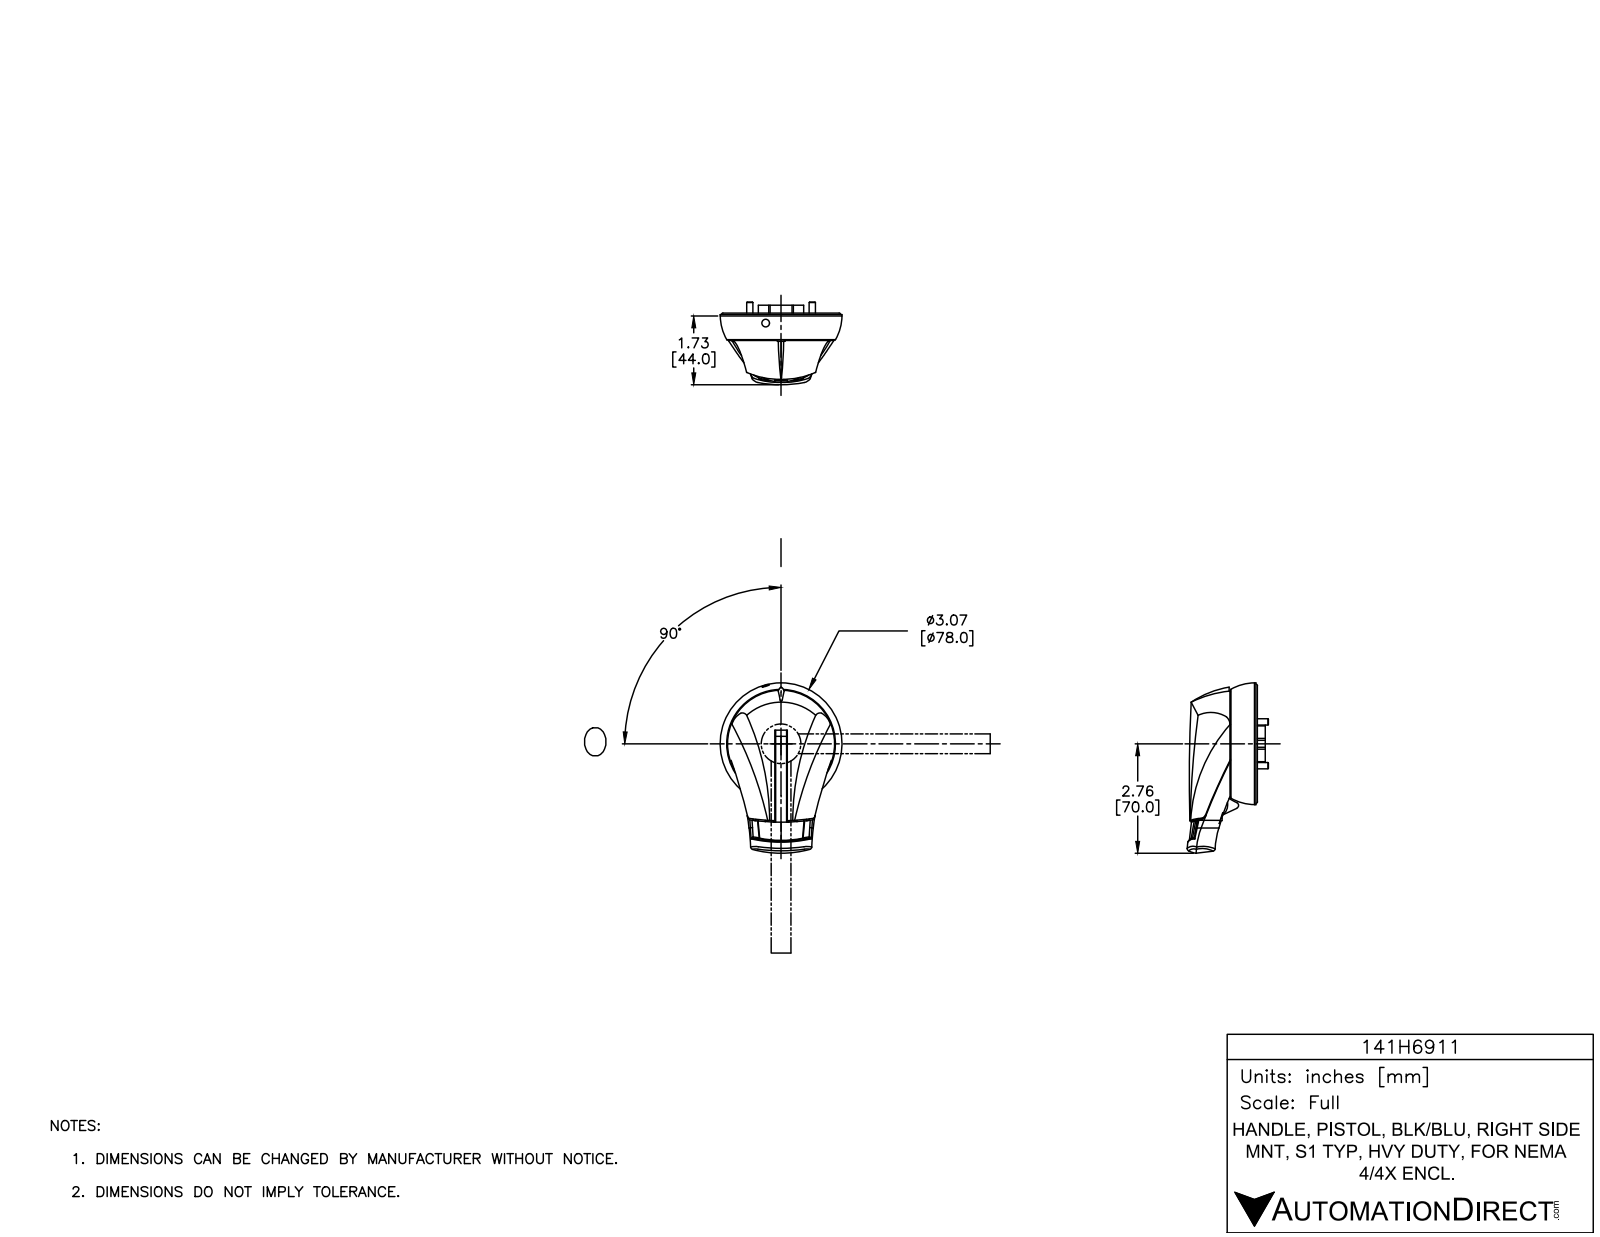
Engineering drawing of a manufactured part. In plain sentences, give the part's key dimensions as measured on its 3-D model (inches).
The part is named "141H6911". Its 3-D file was written by "SolidWorks 2015 (AUTOMOTIVE_DESIGN)". It is 8 solids with 1516 faces: 810 planar, 548 cylindrical and 158 other. Overall it measures 4.291 by 3.07 by 2.046 inches. Its volume is 7.72 cubic inches and its surface area 79.65 square inches. Round holes: 6 of diameter 0.157, 4 of diameter 0.339, 4 of diameter 0.425, 3 of diameter 0.03, 2 of diameter 0.169, 2 of diameter 0.362, 1 of diameter 0.118, 1 of diameter 0.189, 1 of diameter 2.992. Round bosses or shafts: 11 of diameter 0.02, 4 of diameter 0.335, 4 of diameter 0.315, 3 of diameter 0.089, 3 of diameter 0.069, 2 of diameter 0.228, 1 of diameter 2.819, 1 of diameter 2.701. Partial cylindrical surfaces (rounded edges, fillets, slot ends): 221 of radius 0.01, 20 of radius 0.015, 20 of radius 0.034, 15 of radius 0.03, 4 of radius 0.039, 3 of radius 0.025, 3 of radius 5.437, 2 of radius 0.079. The main face-to-face distances are 0.024, 0.701, 0.713, 0.689, 0.035, 0.102, 0.276, 0.173, 0.244, 0.047. The hole center spacings are 0.961, 0.309, 0.669, 1.098, 1.102, 1.203, 1.575, 1.881.
